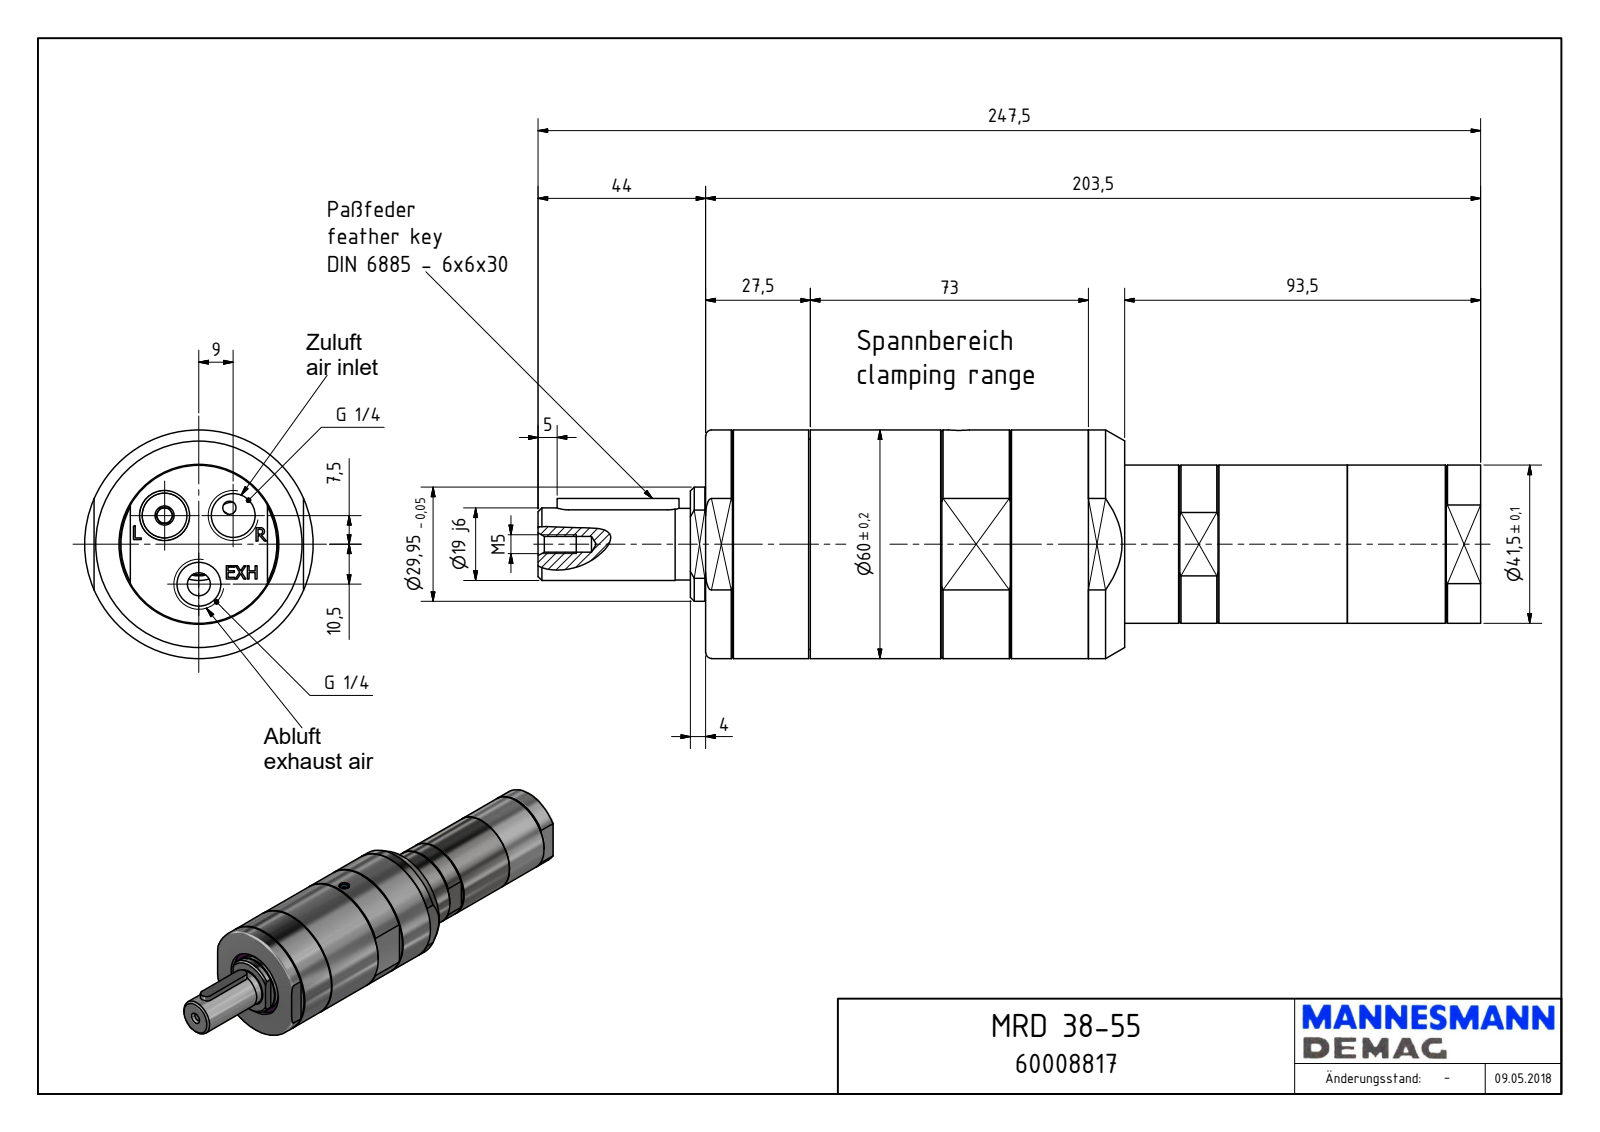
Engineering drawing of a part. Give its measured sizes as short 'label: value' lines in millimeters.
name: MRD 38-55_60008817
written by: Autodesk Inventor 2018 (AUTOMOTIVE_DESIGN)
unit: mm
bodies: 1 solid, 210 faces (122 planar, 39 cylindrical, 49 other)
size: 247.5 × 60 × 60
volume: 443 420 mm³; area: 44 958 mm²
holes: 3× ⌀11.45, 2× ⌀4, 1× ⌀1.55, 1× ⌀4.13, 1× ⌀5.5, 1× ⌀35, 1× ⌀42, 1× ⌀55.38
bosses: 1× ⌀60, 1× ⌀55.18, 1× ⌀41.5, 1× ⌀29.95, 1× ⌀19, 1× ⌀18.8, 1× ⌀5, 1× ⌀3.6
rounds: 2× R3, 1× R25.41
face distances: 93.5, 203.5, 110, 55, 9.5, 27.5, 82.5, 176, 31, 1
hole spacings: 11.72, 20.12, 10.5, 18
